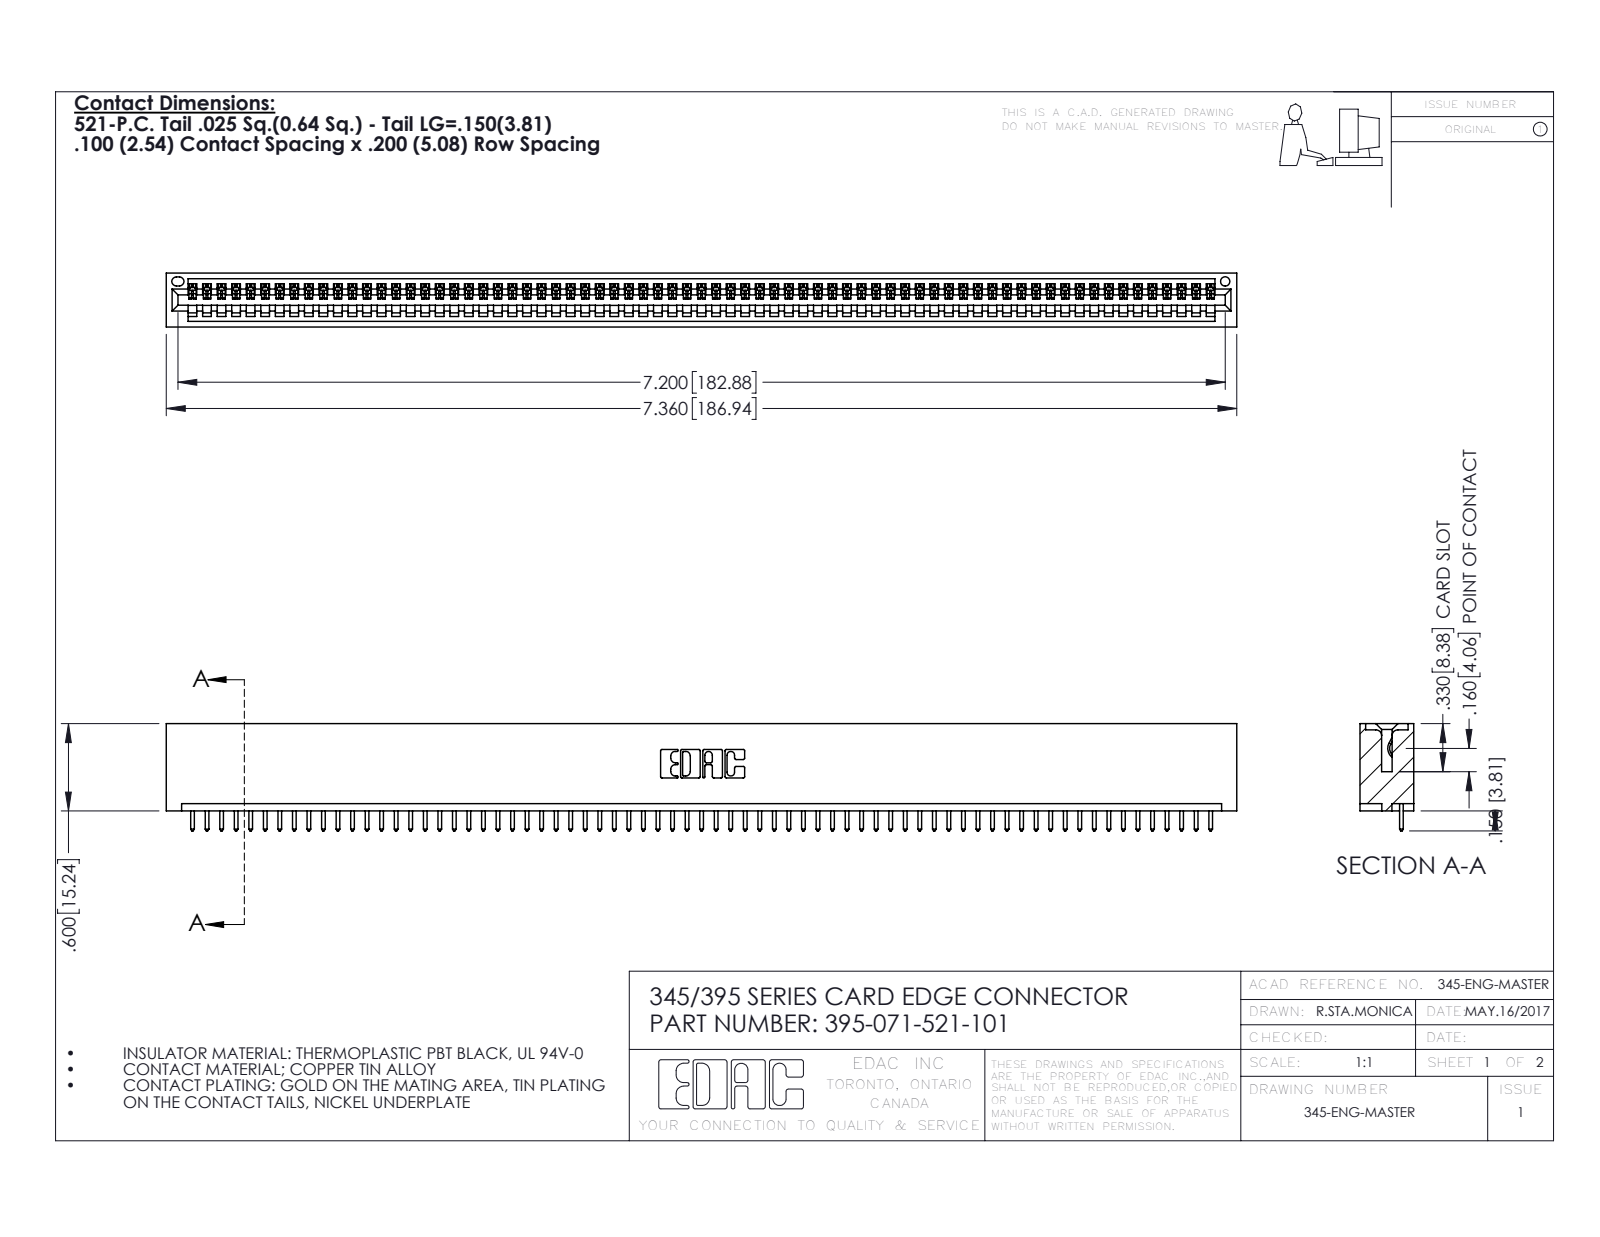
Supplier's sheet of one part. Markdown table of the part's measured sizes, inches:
| quantity | value |
| --- | --- |
| part name | 395-071-521-101; 345 Part_No Mounting Lugs; 345-292-001_345-293-121 |
| STEP written by | SolidWorks 2016 (CONFIG_CONTROL_DESIGN) |
| units | inches |
| bodies | 72 solids, 4236 faces (2916 planar, 1320 cylindrical, 0 other) |
| overall size | 7.36 × 0.737 × 0.37 |
| volume | 1.121 in³ |
| surface area | 37.53 in² |
| round holes (diameter × count) | 0.064 × 1 |
| partial cylindrical surfaces (radius × count) | 0.006 × 142, 0.01 × 142, 0.01 × 22, 0.007 × 6, 0.031 × 6, 0.026 × 3, 0.031 × 2, 0.04 × 2 |
| main face-to-face distances | 0.298, 0.072, 0.37, 0.2, 0.098, 0.272, 0.025, 0.225, 0.149, 0.072 |
